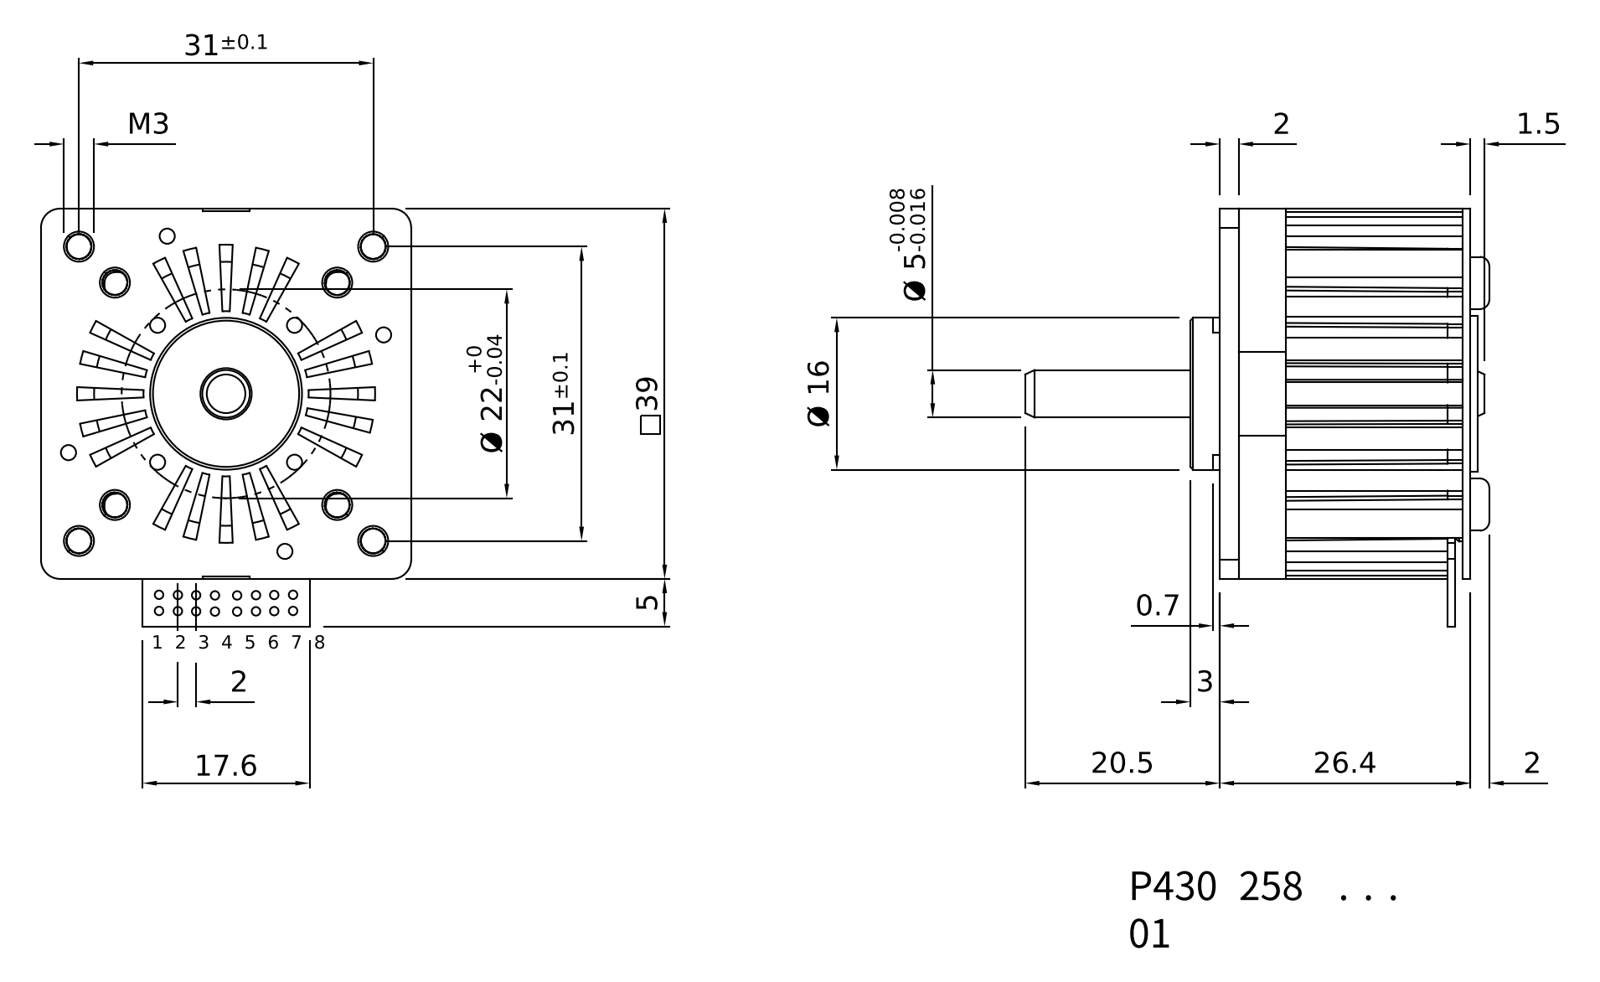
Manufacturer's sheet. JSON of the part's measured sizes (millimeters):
{"part_name": "2800400007_D_FAUT; 2800400008_D_FAUT; 2610400001Z_D_FAUT_ASM; 2800400009_D_FAUT (+8 more)", "step_written_by": "PRO/ENGINEER BY PARAMETRIC TECHNOLOGY CORPORATION, 2014310 (CONFIG_CONTROL_DESIGN)", "units": "millimeters", "bodies": {"solids": 10, "faces": 991, "planar": 523, "cylindrical": 378, "other": 90}, "overall_size": [48.76, 44, 39], "volume_mm3": 29632, "surface_area_mm2": 20358, "round_holes": [[0.8, 16], [1.6, 12], [2.2, 8], [2.5, 8], [0.4, 6], [3.1, 4], [3.21, 4], [5.4, 1], [8, 1], [15, 1], [16.2, 1], [16.3, 1]], "round_bosses_or_shafts": [[1.2, 6], [5.5, 4], [1.5, 4], [39, 1], [16.4, 1], [16, 1], [5, 1]], "partial_cylinders_radius": [[0.3, 68], [0.5, 16], [0.2, 12], [2.5, 10], [1, 4], [2, 4], [2.4, 4], [10.5, 1]], "face_to_face_distances": [0.8, 1.6, 2.4, 22, 2, 24, 1.1, 25.6, 23.6, 24.4], "hole_center_spacings": [2, 2.62, 4, 4.35, 6, 6.24, 1.7, 8]}
